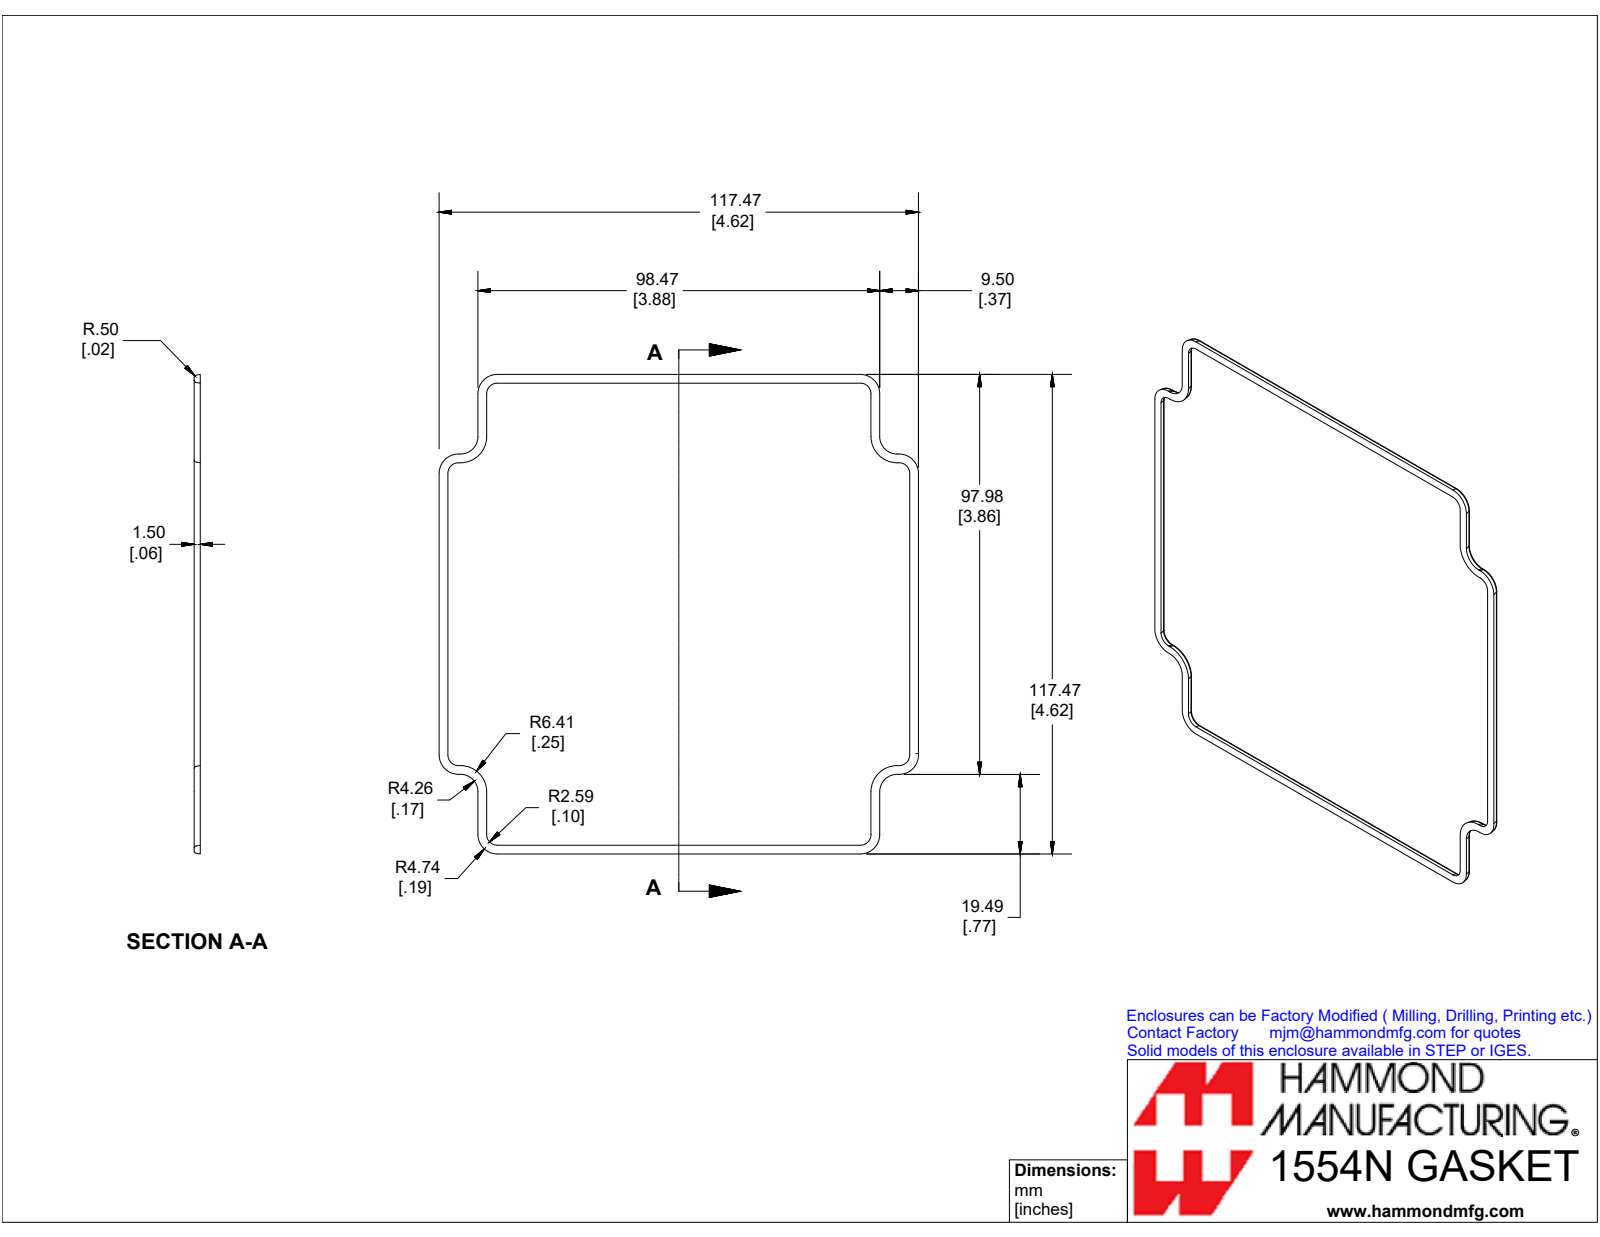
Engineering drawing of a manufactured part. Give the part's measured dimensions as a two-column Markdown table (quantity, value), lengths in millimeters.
| quantity | value |
| --- | --- |
| part name | 1554NGASKET |
| STEP written by | SolidWorks 2019 (CONFIG_CONTROL_DESIGN) |
| units | millimeters |
| bodies | 1 solid, 98 faces (26 planar, 24 cylindrical, 48 other) |
| overall size | 117.7 × 117.7 × 1.7 |
| volume | 1 400 mm³ |
| surface area | 3 032 mm² |
| partial cylindrical surfaces (radius × count) | 0.5 × 16 |
| main face-to-face distances | 113.8, 1.7, 9.4, 104.4, 95, 19.2, 94.6, 75.4 |
